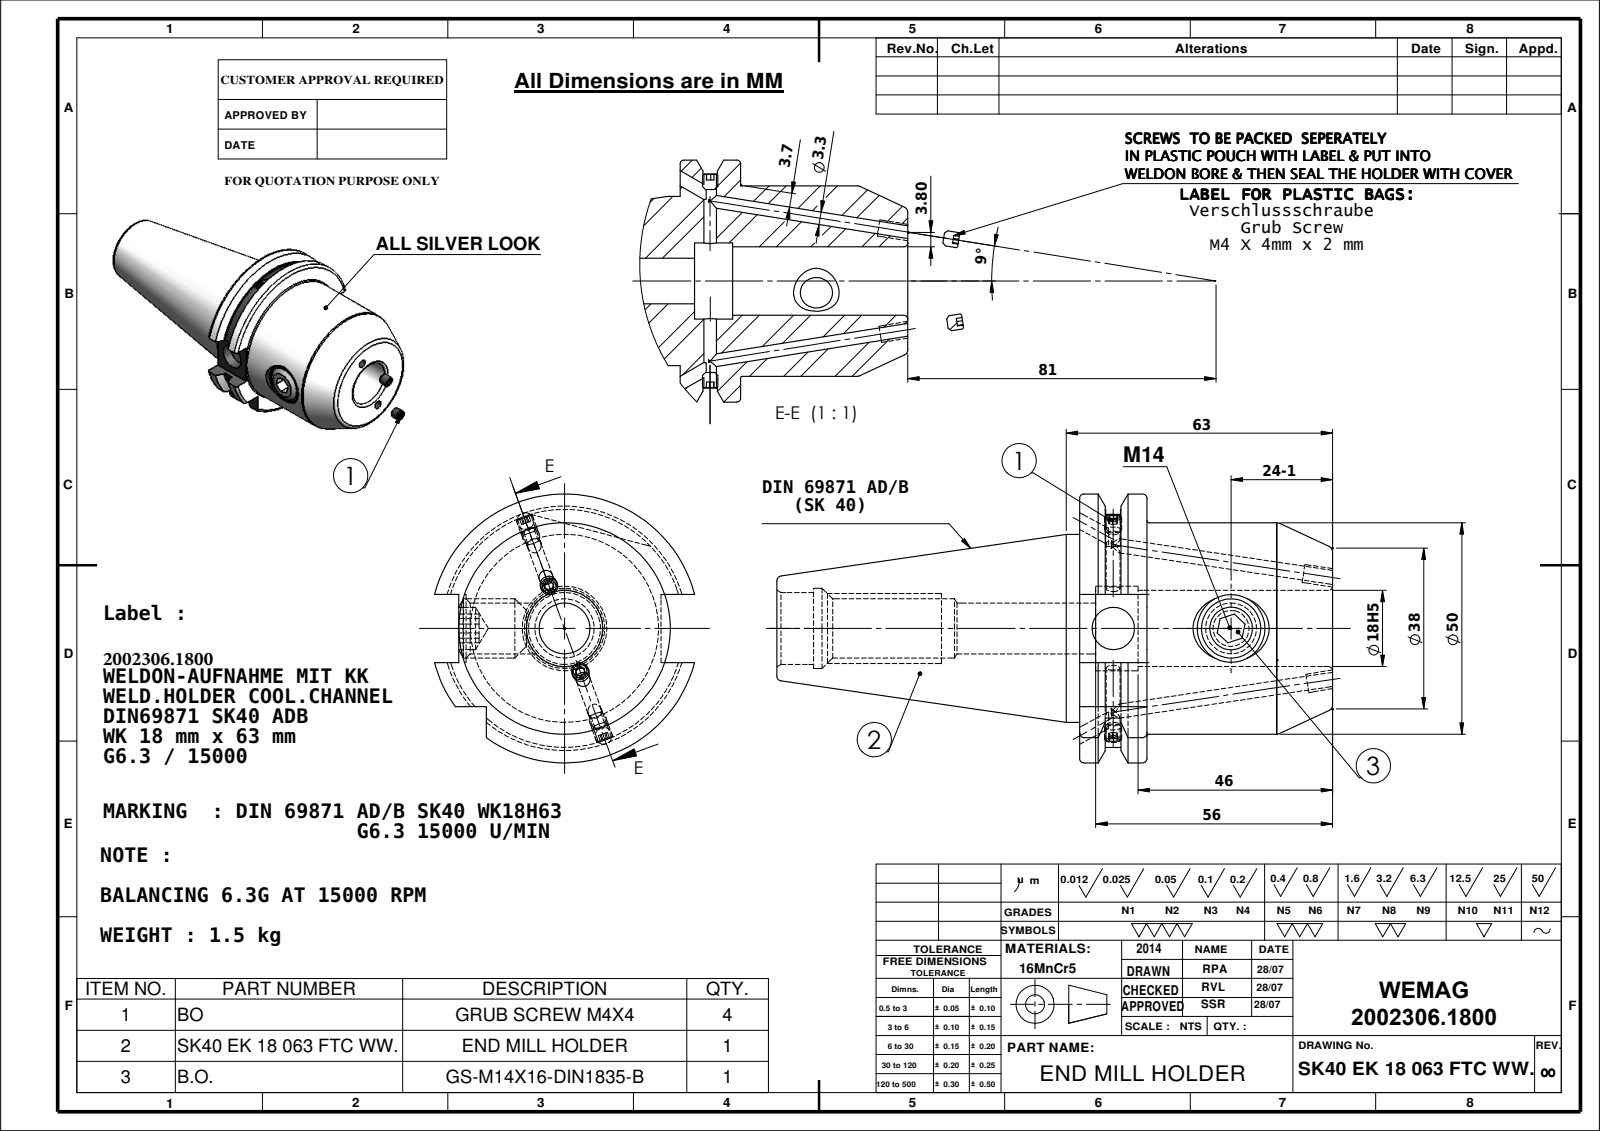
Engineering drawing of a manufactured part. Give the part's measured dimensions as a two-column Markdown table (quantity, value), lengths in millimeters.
| quantity | value |
| --- | --- |
| part name | SK40 EK 18 063 FTC WW.; M14X16_ISO 4026 - M12 x 12-N; Copy of M4X4_DIN 913 - M4 x 4-N |
| STEP written by | SolidWorks 2009 (CONFIG_CONTROL_DESIGN) |
| units | millimeters |
| bodies | 6 solids, 207 faces (80 planar, 58 cylindrical, 69 other) |
| overall size | 146.04 × 63.55 × 61.48 |
| volume | 166 563 mm³ |
| surface area | 32 489 mm² |
| round holes (diameter × count) | 3.3 × 3, 12 × 2, 10 × 1, 14 × 1, 16 × 1, 17 × 1, 18 × 1, 19 × 1, 20 × 1 |
| round bosses / shafts (diameter × count) | 4 × 4, 50 × 1, 44.45 × 1, 14 × 1 |
| partial cylindrical surfaces (radius × count) | 28.12 × 1, 31.77 × 1 |
| main face-to-face distances | 15.9, 59.8, 43.9, 47.8, 3.8, 12.1, 56, 16.1, 71.6, 75.4 |
| hole center spacings | 27.85 |
